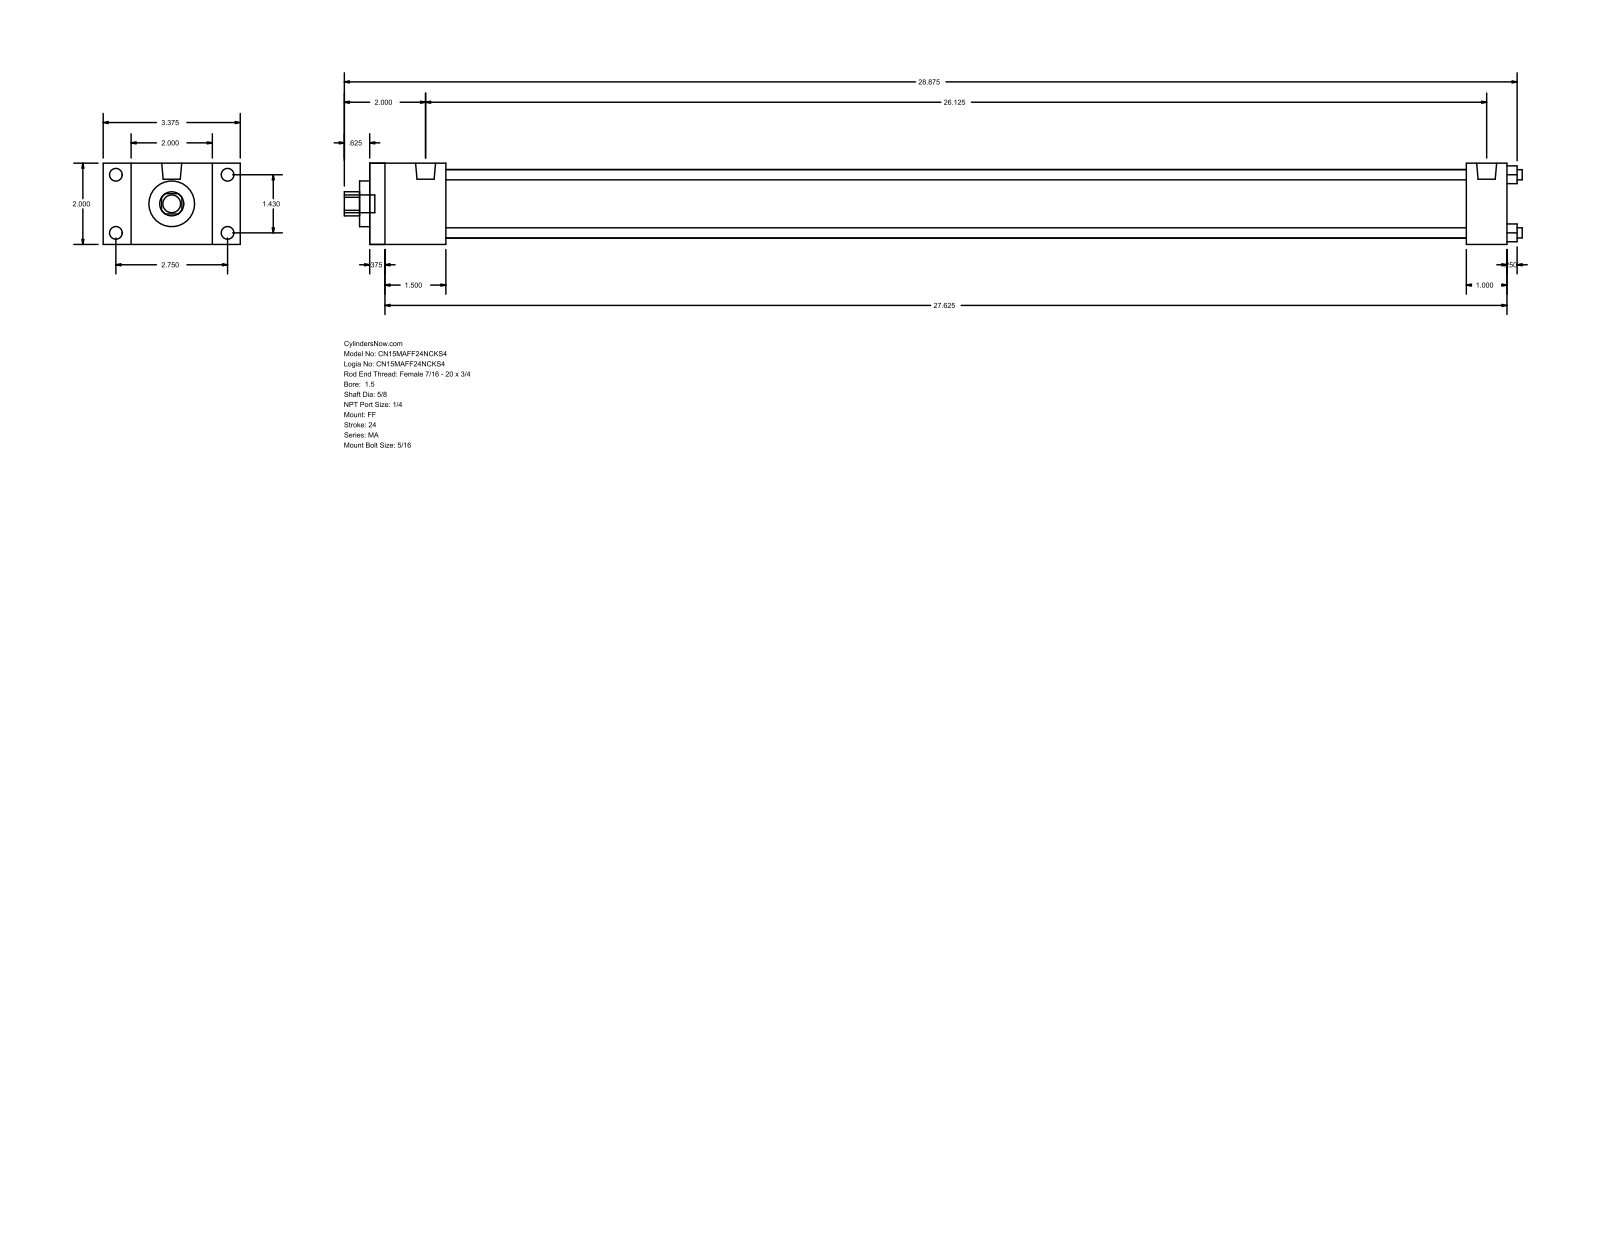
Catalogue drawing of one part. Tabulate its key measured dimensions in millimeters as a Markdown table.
| quantity | value |
| --- | --- |
| part name | MA_FF__0150_0.625 |
| STEP written by | GSSL Pune (CONFIG_CONTROL_DESIGN) |
| units | millimeters |
| bodies | 0 solids, 92 faces (64 planar, 28 cylindrical, 0 other) |
| overall size | 736.6 × 85.72 × 50.8 |
| round holes (diameter × count) | 6.35 × 4, 15.88 × 1, 28.57 × 1, 42.93 × 1 |
| round bosses / shafts (diameter × count) | 7.94 × 8, 12.49 × 2, 11.11 × 1 |
| partial cylindrical surfaces (radius × count) | 7.54 × 1 |
| main face-to-face distances | 50.8, 711.2, 9.52, 701.68, 47.62, 685.79, 38.1, 676.27, 638.17, 663.58 |
| hole center spacings | 25.68, 36.32, 51.36 |
